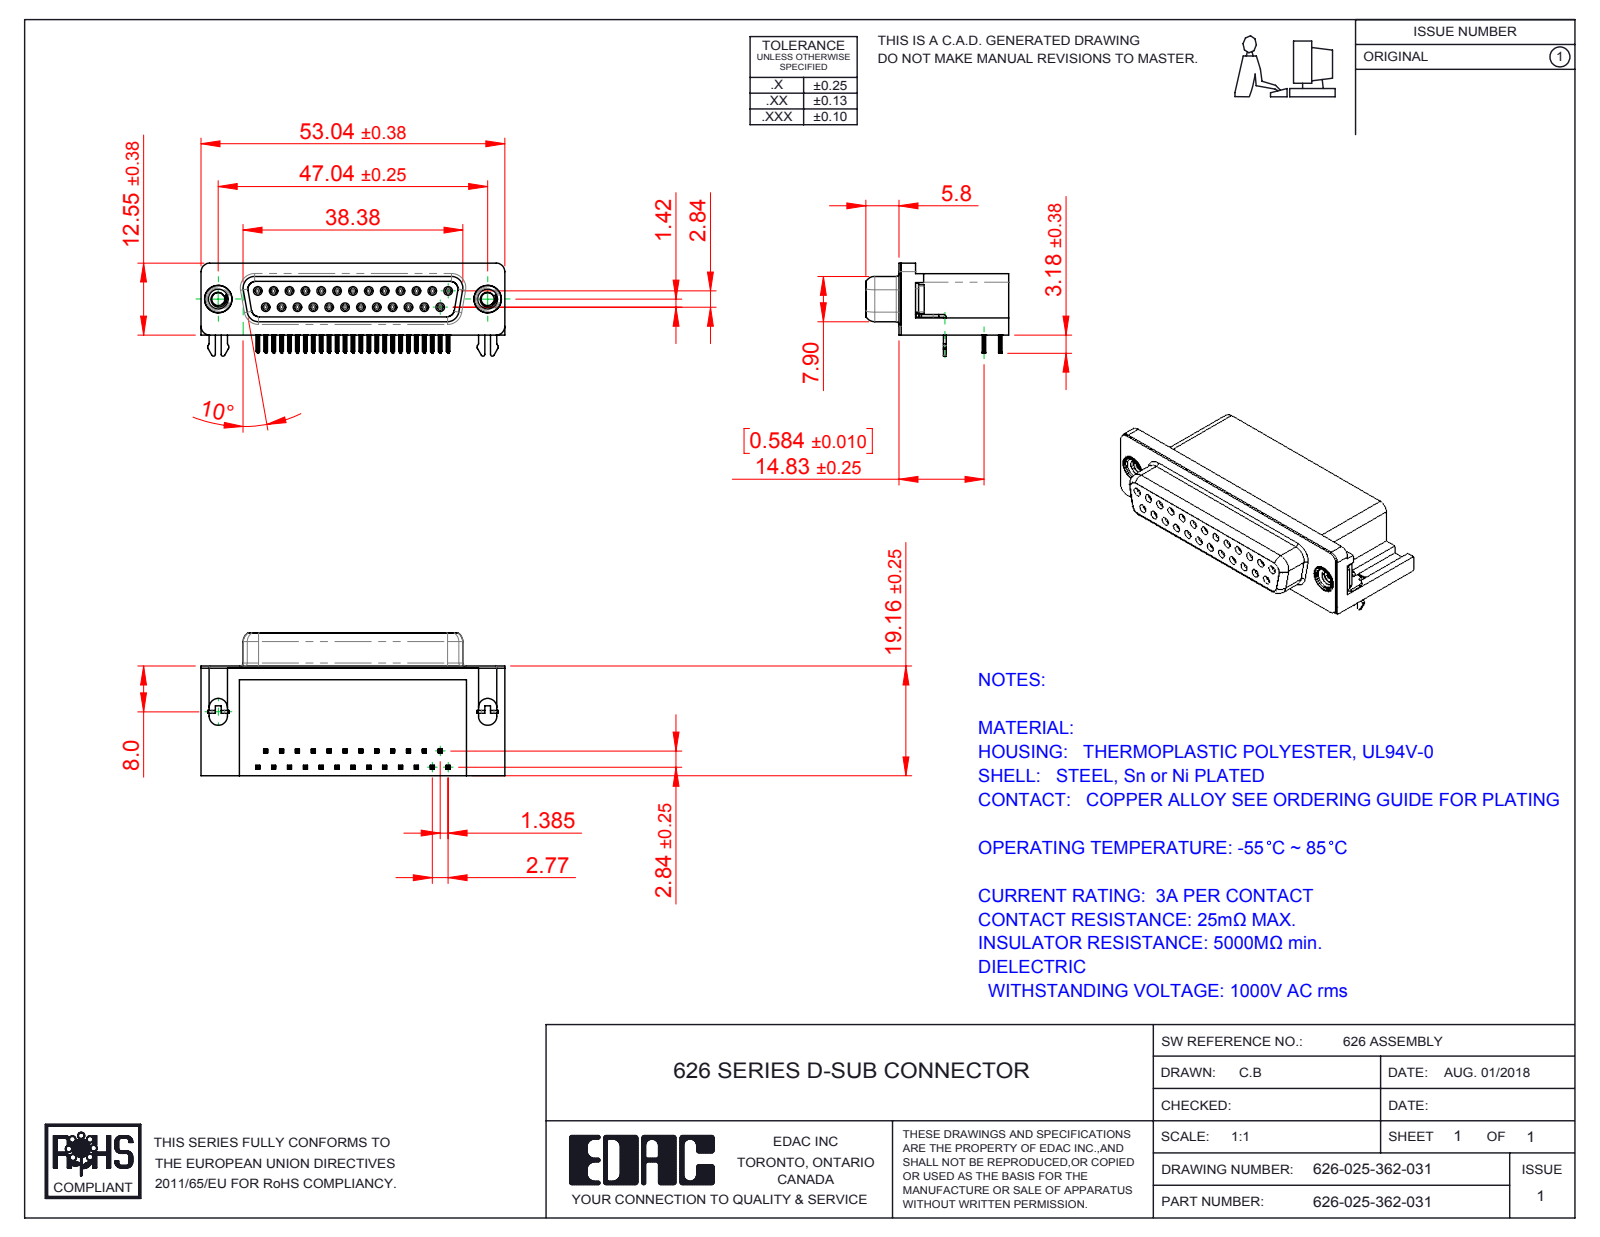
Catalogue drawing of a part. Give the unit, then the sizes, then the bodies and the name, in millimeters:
Units: millimetres
Overall size (bounding box): 53.04 × 24.96 × 16.25
Round holes (diameter × count): ⌀0.8 ×25, ⌀0.9 ×25, ⌀2.26 ×2, ⌀4 ×2, ⌀4.8 ×2, ⌀5 ×2
Round bosses / shafts (diameter × count): ⌀1.2 ×25, ⌀4.9 ×2, ⌀4.75 ×2, ⌀3.9 ×2
Partial cylindrical surfaces — rounded edges, fillets, slot ends (radius × count): R0.1 ×200, R0.15 ×100, R0.35 ×50, R0.34 ×25, R1 ×18, R0.28 ×12, R0.5 ×10, R0.25 ×8
Main face-to-face distances: 10.35, 0.4, 18.76, 6.2, 2.73, 2.84, 9.38, 3.18, 0.35, 0.85
Hole centre spacings: 3.16, 2.77, 5.54, 8.31, 11.08, 5.03, 5.04, 7.48
Volume: 10 670 mm³ · Surface area: 11 371 mm²
Bodies: 31 solids, 3890 faces (1754 planar, 928 cylindrical, 1208 other)
Part name (STEP PRODUCT): 626 Contact Bottom; 626 Housing_25 Socket; 626-025-362-031; 626 Contact Top (+3 more)
STEP written by: SolidWorks 2016 (CONFIG_CONTROL_DESIGN)
